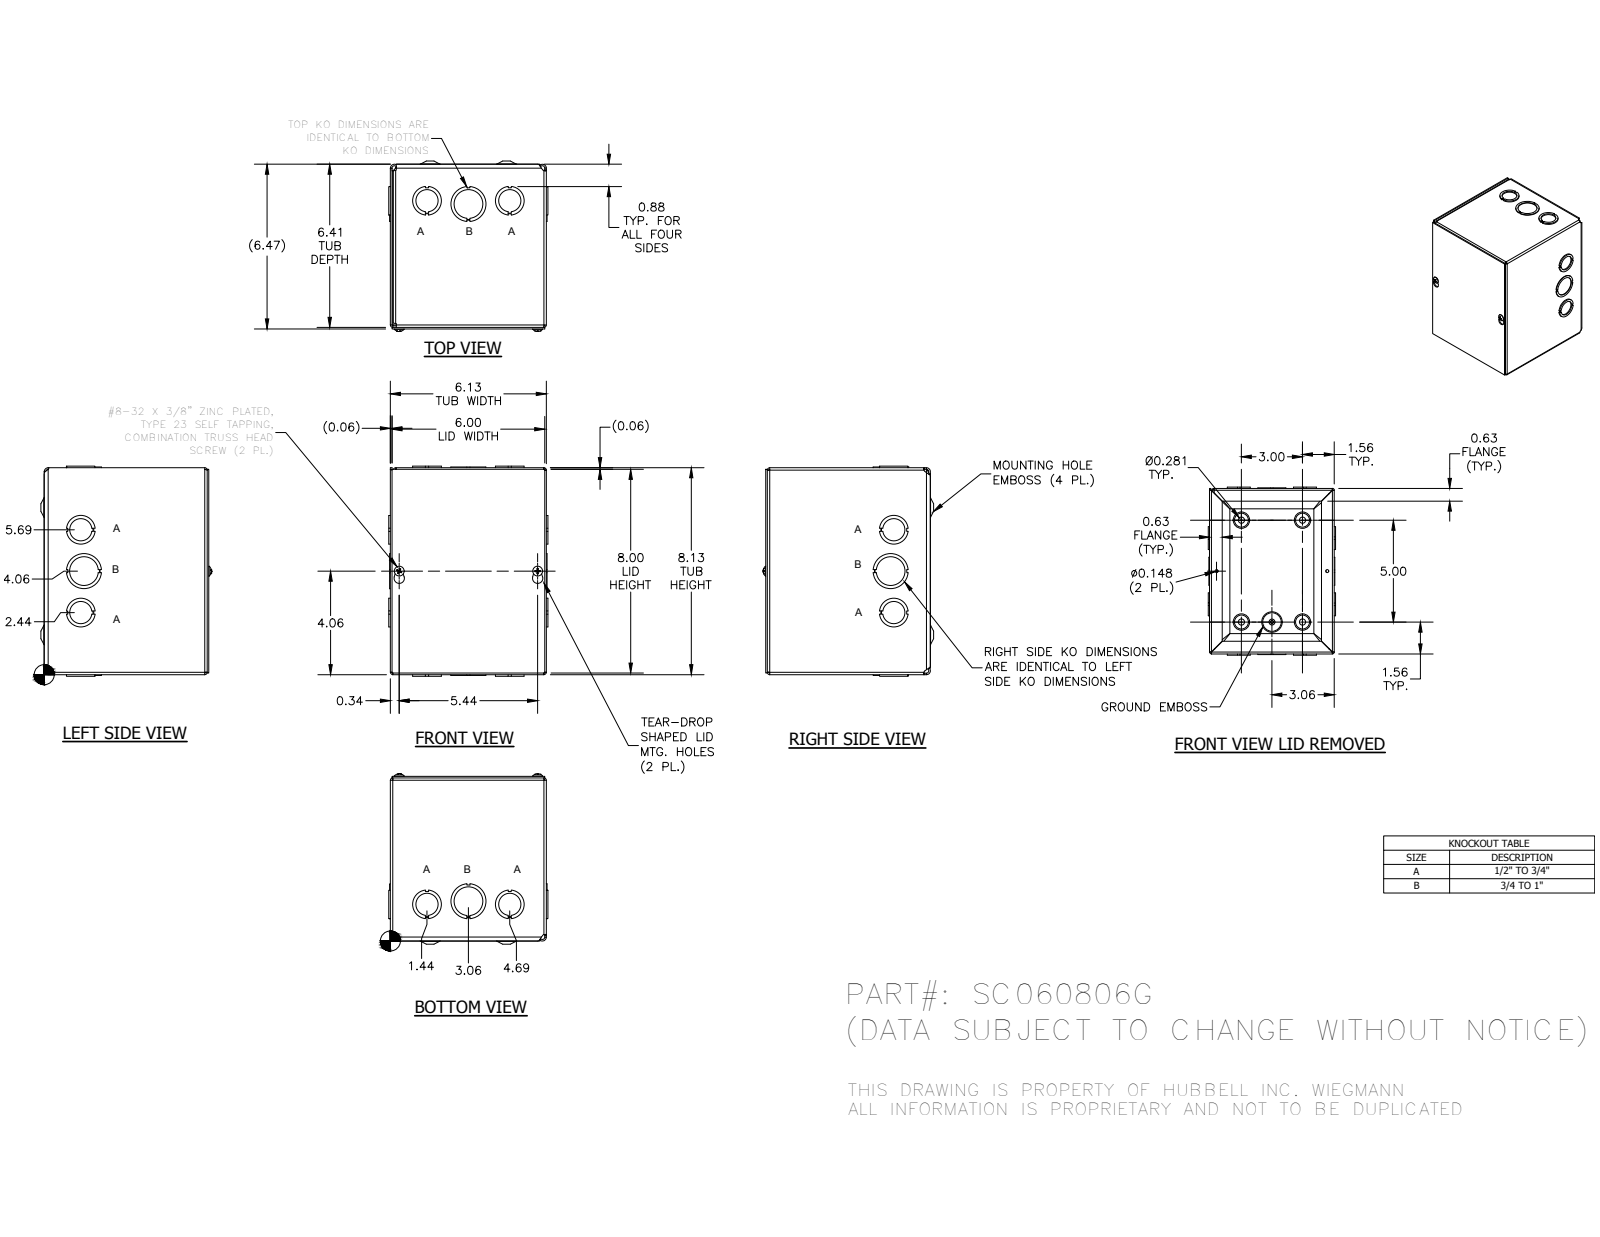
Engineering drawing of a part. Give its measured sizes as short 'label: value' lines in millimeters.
name: SC0608GBKP; SC060806GWRA; SC0608GLID; 34056 (+1 more)
written by: Autodesk Inventor 2014 (AUTOMOTIVE_DESIGN)
unit: mm
bodies: 20 solids, 630 faces (374 planar, 135 cylindrical, 121 other)
size: 209.53 × 170 × 158.72
holes: 6× ⌀28.57, 4× ⌀7.62, 4× ⌀22.22, 2× ⌀3.76, 2× ⌀34.92, 1× ⌀4.19
bosses: 2× ⌀9.75, 2× ⌀4.17, 1× ⌀5.8
rounds: 8× R0.79, 8× R2.37, 4× R1.4, 4× R1.57, 4× R2.38, 4× R2.79, 4× R2.97, 4× R3.15
face distances: 1.57, 154, 161.12, 1.58, 155.57, 162.69, 152.43, 1.59, 162.71, 164.28
hole spacings: 38.1, 41.39, 41.4, 70.64, 70.65, 76.2, 82.55, 124.55
